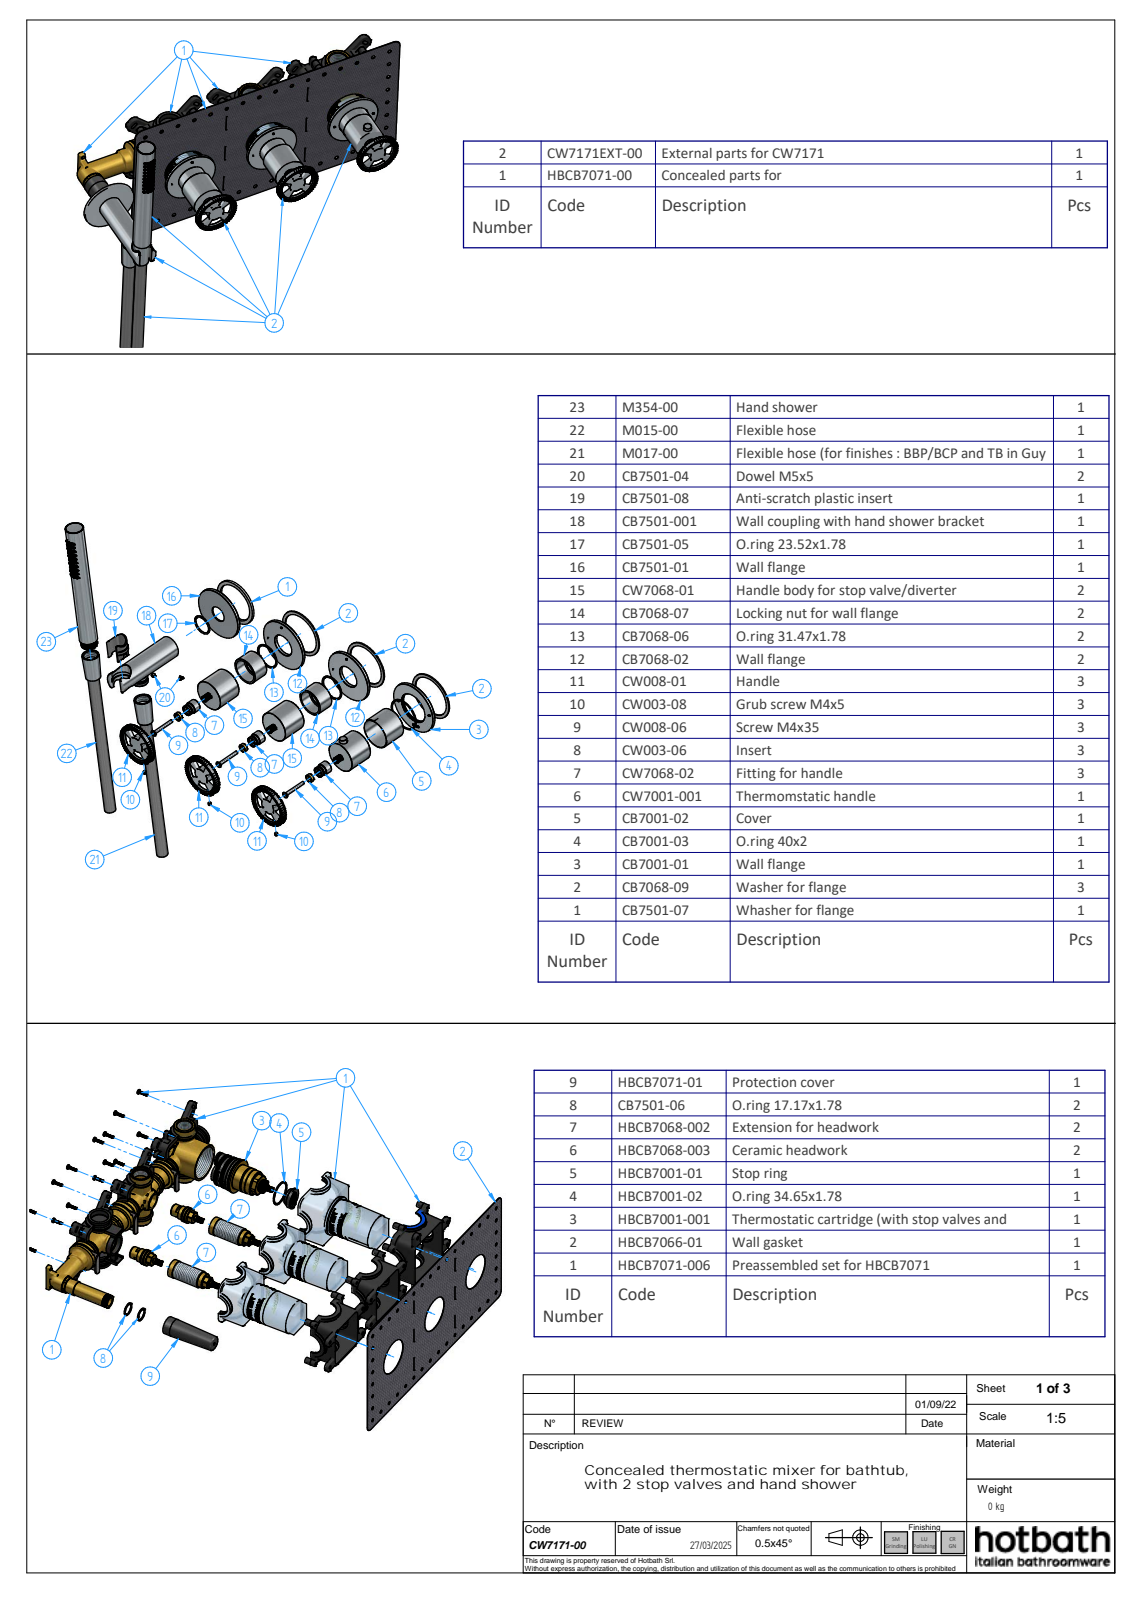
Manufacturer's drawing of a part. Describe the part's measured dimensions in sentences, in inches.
The part is named "CW7171EXT-00; CW008-01; CB7501-04; CB7501-01 (+8 more)". Its 3-D file was written by "Solid Edge (AUTOMOTIVE_DESIGN)". It is 30 solids with 6360 faces: 920 planar, 1887 cylindrical and 3553 other. Overall it measures 18.252 by 14.799 by 13.614 inches. Its volume is 17.74 cubic inches and its surface area 312.6 square inches. Round holes: 41 of diameter 0.126, 4 of diameter 0.197, 3 of diameter 0.128, 3 of diameter 0.177, 3 of diameter 0.287, 3 of diameter 0.445, 3 of diameter 0.453, 3 of diameter 0.472, 3 of diameter 0.591, 3 of diameter 1.516, 3 of diameter 2.638, 2 of diameter 0.163. Round bosses or shafts: 6 of diameter 0.551, 4 of diameter 2.835, 4 of diameter 1.654, 4 of diameter 0.63, 3 of diameter 2.244, 3 of diameter 0.866, 3 of diameter 0.492, 3 of diameter 0.157. Partial cylindrical surfaces (rounded edges, fillets, slot ends): 346 of radius 0.008, 336 of radius 0.024, 336 of radius 0.311, 50 of radius 0.039, 48 of radius 0.004, 8 of radius 0.02, 6 of radius 0.012, 4 of radius 0.014. The main face-to-face distances are 0.157, 0.156, 0.159, 0.039, 0.118, 1.965, 1.967, 2.123, 2.125, 0.159. The hole center spacings are 0.236, 0.284, 0.498, 0.472, 0.726, 0.709, 0.958, 0.157.
